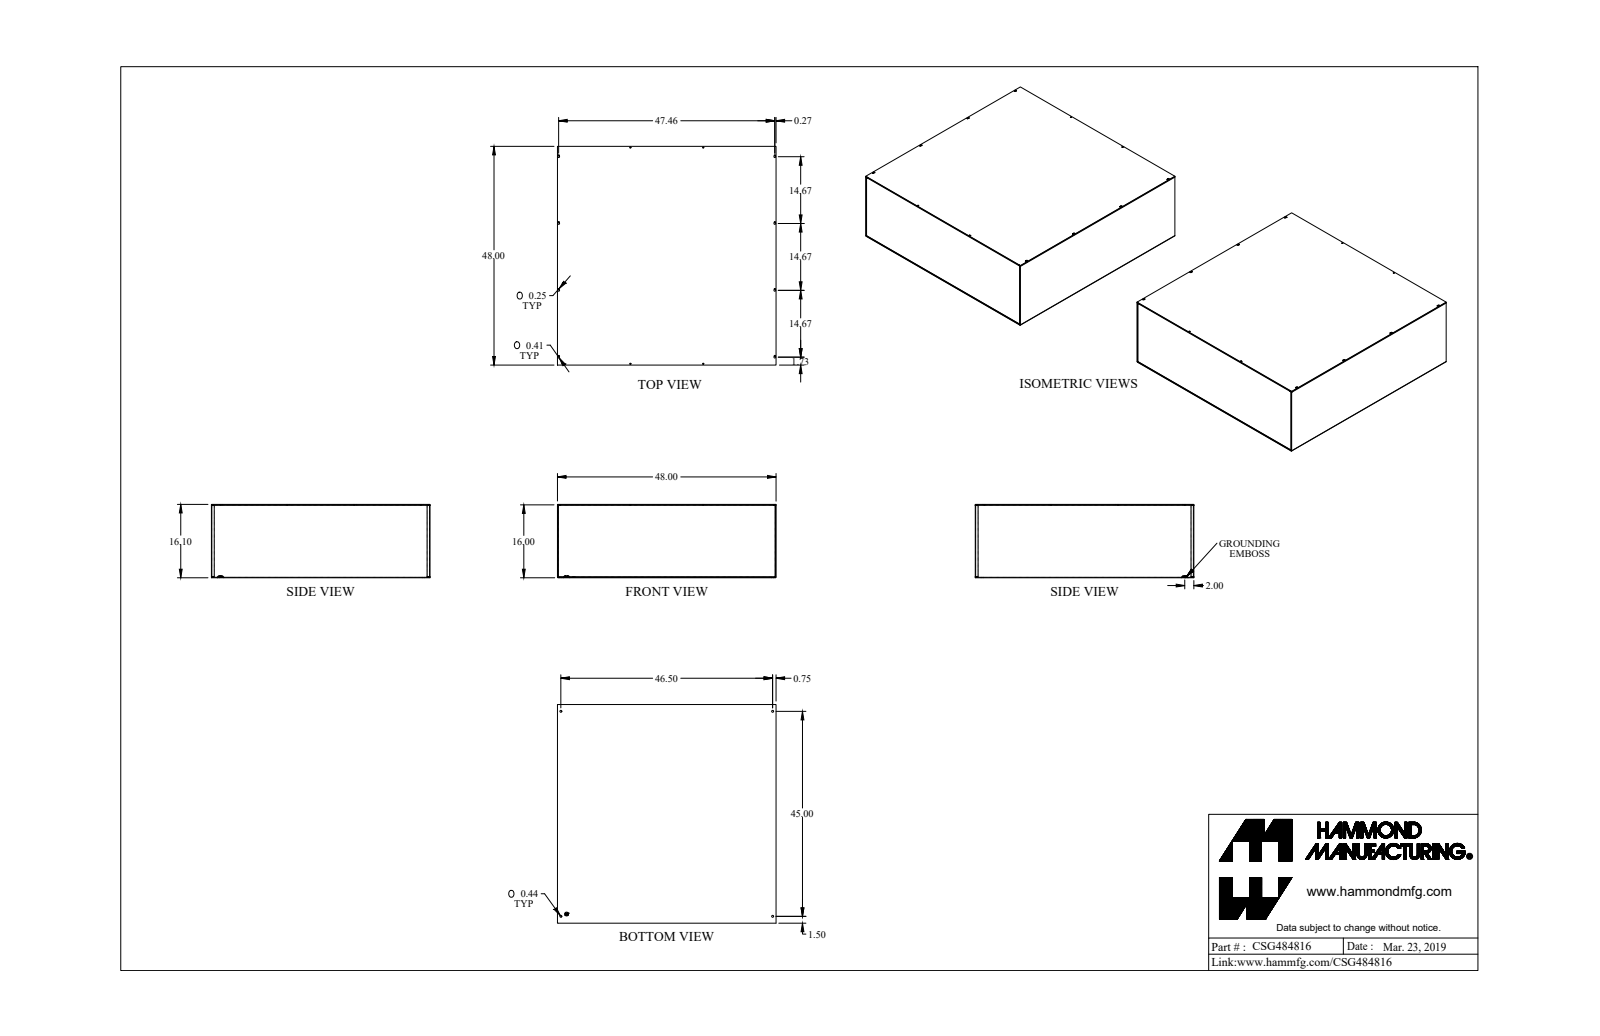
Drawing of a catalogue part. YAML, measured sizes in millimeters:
part_name: "CSG484816_Default"
step_written_by: "SolidWorks 2019 (CONFIG_CONTROL_DESIGN)"
units: millimeters
bodies: {solids: 4, faces: 245, planar: 125, cylindrical: 112, other: 8}
overall_size: [1219.2, 1219.2, 408.8]
volume: 12130000
surface_area: 10100000
round_holes:
  - {diameter: 4.3, count: 13}
  - {diameter: 6.4, count: 4}
  - {diameter: 11.1, count: 4}
  - {diameter: 12.7, count: 1}
round_bosses_or_shafts:
  - {diameter: 12.5, count: 1}
  - {diameter: 9.1, count: 1}
partial_cylinders:
  - {radius: 1.2, count: 12}
  - {radius: 3.6, count: 12}
  - {radius: 2.4, count: 8}
  - {radius: 3.2, count: 8}
  - {radius: 5.2, count: 8}
face_to_face_distances: [2.4, 406.4, 1216.8, 404, 408.8, 1219.2, 1214.4, 4.8, 401.6, 2.7]
hole_center_spacings: [1205.5, 1261.7, 17.6, 372.5, 385.4, 388.6, 402, 577.1]
